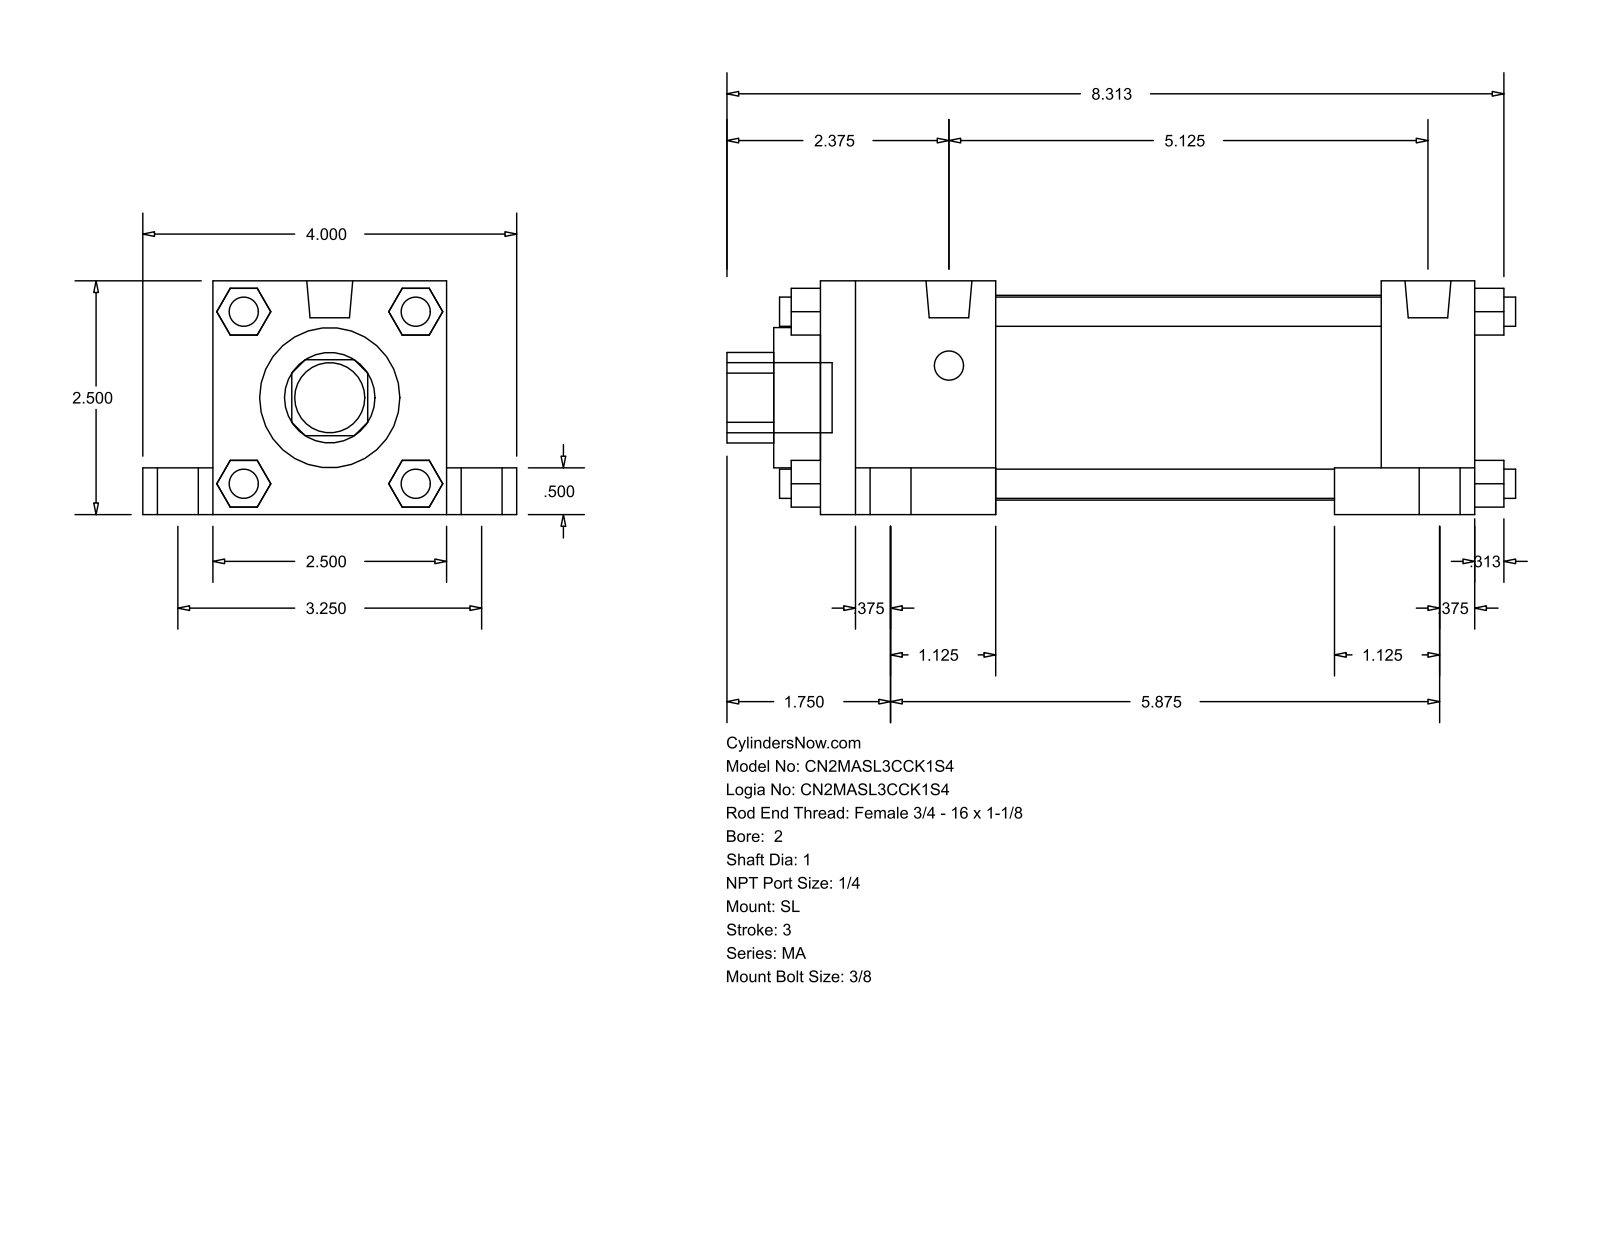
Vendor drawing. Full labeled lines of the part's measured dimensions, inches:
Part name (STEP PRODUCT): MA_SL__0200_1
STEP written by: GSSL Pune (CONFIG_CONTROL_DESIGN)
Units: inches
Bodies: 0 solids, 148 faces (112 planar, 36 cylindrical, 0 other)
Overall size (bounding box): 8.437 × 4 × 2.5
Round holes (diameter × count): ⌀1 ×1, ⌀1.5 ×1, ⌀2.19 ×1
Round bosses / shafts (diameter × count): ⌀0.313 ×8, ⌀0.687 ×4, ⌀0.437 ×4, ⌀0.492 ×2, ⌀0.75 ×1
Partial cylindrical surfaces — rounded edges, fillets, slot ends (radius × count): R0.484 ×1
Main face-to-face distances: 2.5, 0.5, 7, 0.75, 3.25, 1, 2, 1.875, 5.125, 6
